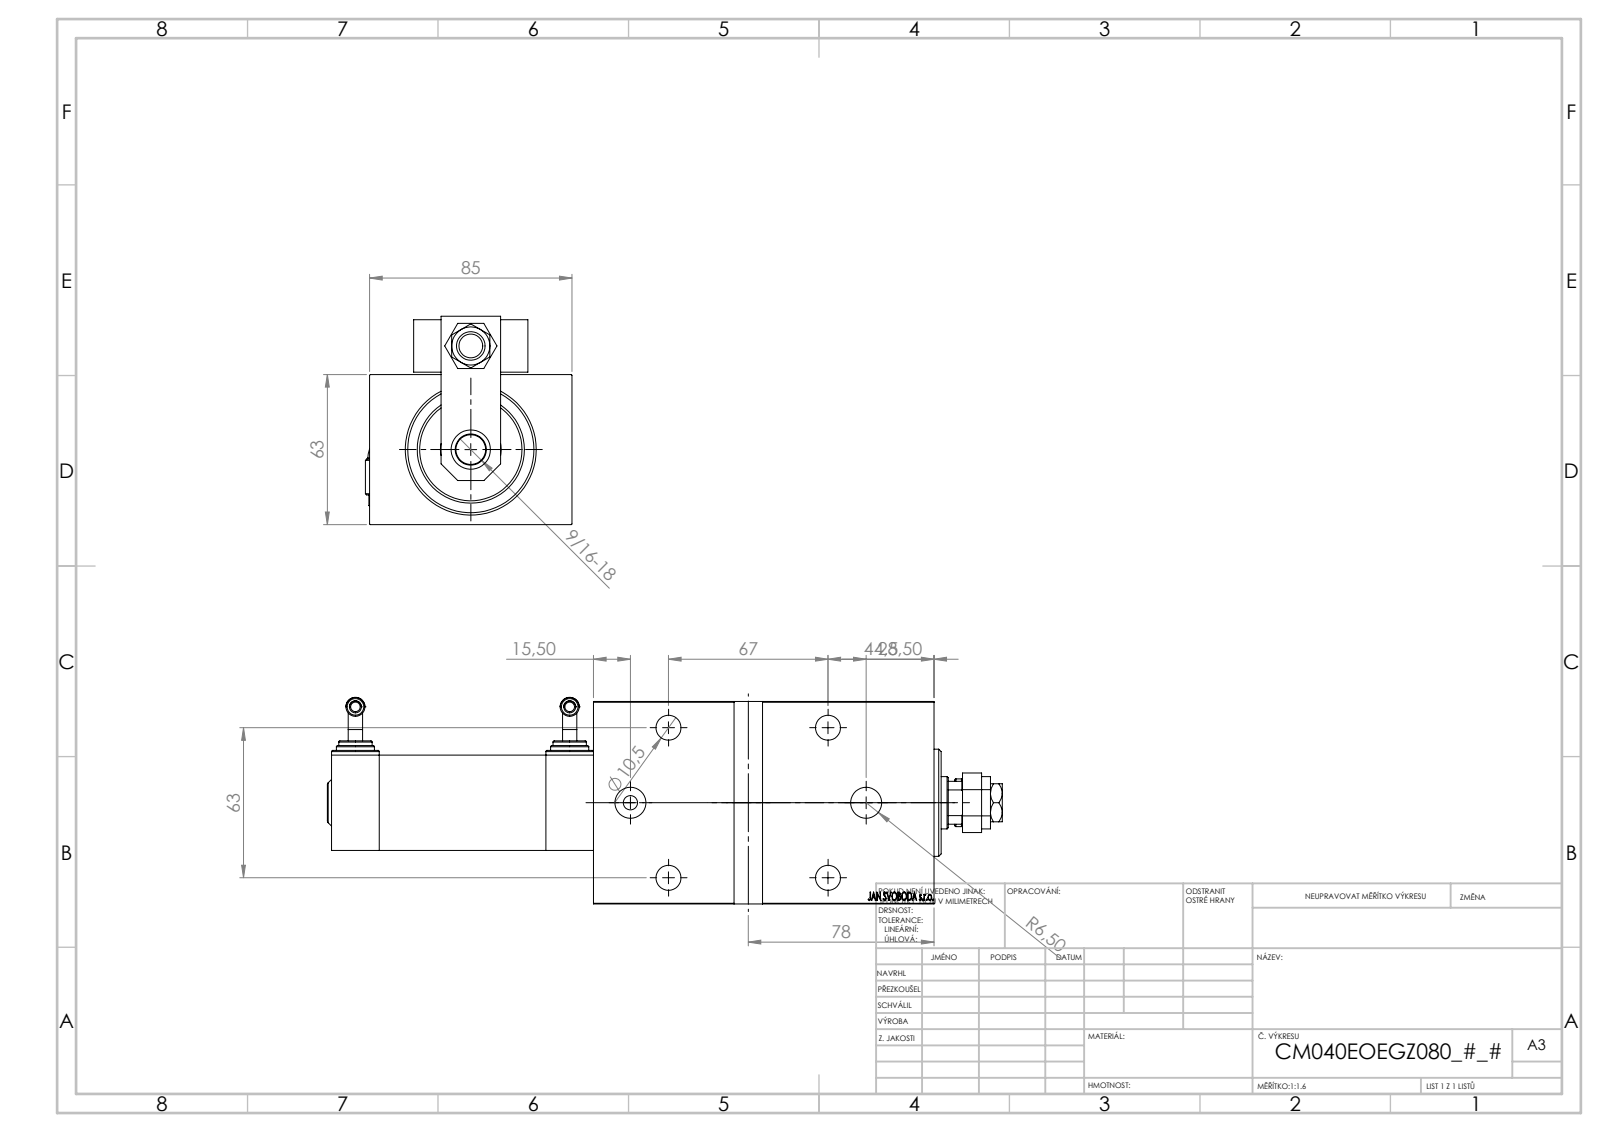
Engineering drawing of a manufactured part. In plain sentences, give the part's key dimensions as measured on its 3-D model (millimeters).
The part is named "V450CM_VC_B; V450CM_E_VCP; SWITCH_P_FRONT_BACK; SWITCH DIM W_B (+7 more)". Its 3-D file was written by "SolidWorks 2019 (CONFIG_CONTROL_DESIGN)". It is 14 solids with 1102 faces: 525 planar, 112 cylindrical and 465 other. Overall it measures 283.5 by 87.5 by 86.76 millimeters. Its volume is 940 114 cubic millimeters and its surface area 163 289 square millimeters. Round holes: 5 of diameter 16.5, 4 of diameter 4, 4 of diameter 8, 4 of diameter 10.5, 3 of diameter 13, 1 of diameter 12, 1 of diameter 12.5, 1 of diameter 14, 1 of diameter 22, 1 of diameter 25.5, 1 of diameter 40, 1 of diameter 53. Round bosses or shafts: 3 of diameter 20, 3 of diameter 6, 2 of diameter 16, 2 of diameter 14, 2 of diameter 8, 2 of diameter 5.04, 1 of diameter 45, 1 of diameter 42. Partial cylindrical surfaces (rounded edges, fillets, slot ends): 1 of radius 3, 1 of radius 10.5. The main face-to-face distances are 63, 85, 22.5, 62.5, 20, 143, 3, 163, 90, 12. The hole center spacings are 35.33, 88.78, 12.81, 20, 23.26, 32.22, 42.79, 47.94.
